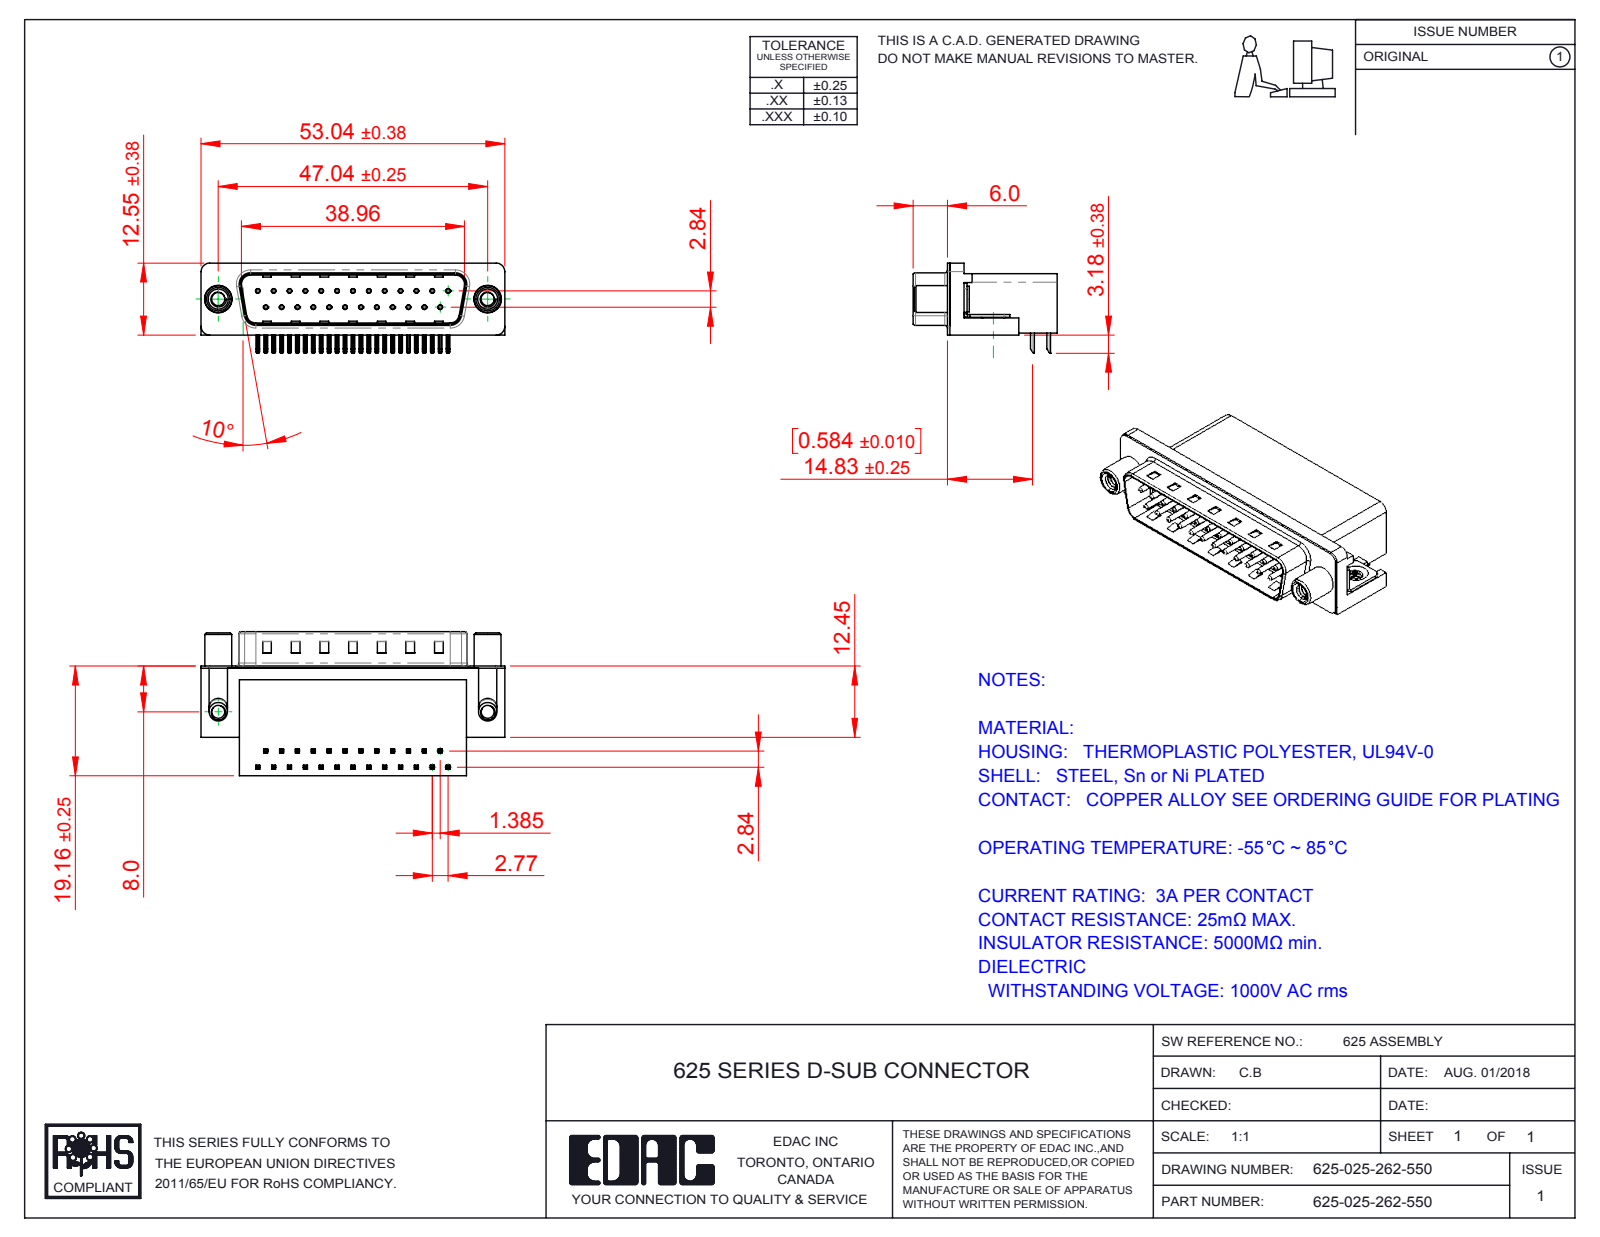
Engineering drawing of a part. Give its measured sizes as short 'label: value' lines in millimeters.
name: 625 4-40 Threaded Board Mount; 625 Round Threaded Standoff; 625-025-262-550; 625 Housing_25 Socket (+3 more)
written by: SolidWorks 2016 (CONFIG_CONTROL_DESIGN)
unit: mm
bodies: 31 solids, 2291 faces (1399 planar, 681 cylindrical, 211 other)
size: 53.04 × 25.16 × 15.73
volume: 9 266 mm³; area: 9 140 mm²
holes: 25× ⌀0.35, 25× ⌀0.8, 2× ⌀2.26, 2× ⌀2.3, 2× ⌀3.1, 2× ⌀4, 2× ⌀4.8, 2× ⌀5
bosses: 25× ⌀0.75, 2× ⌀4.9, 2× ⌀4.7, 2× ⌀4.5, 2× ⌀3.85, 2× ⌀3.26
rounds: 100× R0.25, 50× R0.12, 16× R1, 9× R0.5, 8× R1.6, 7× R1.5, 4× R0.9, 4× R2
face distances: 0.4, 10.35, 18.76, 2.1, 8.76, 10.46, 10.86, 1.7, 19.16, 2.9
hole spacings: 3.16, 2.77, 11.08, 5.54, 8.31, 5.03, 13.85, 7.48
